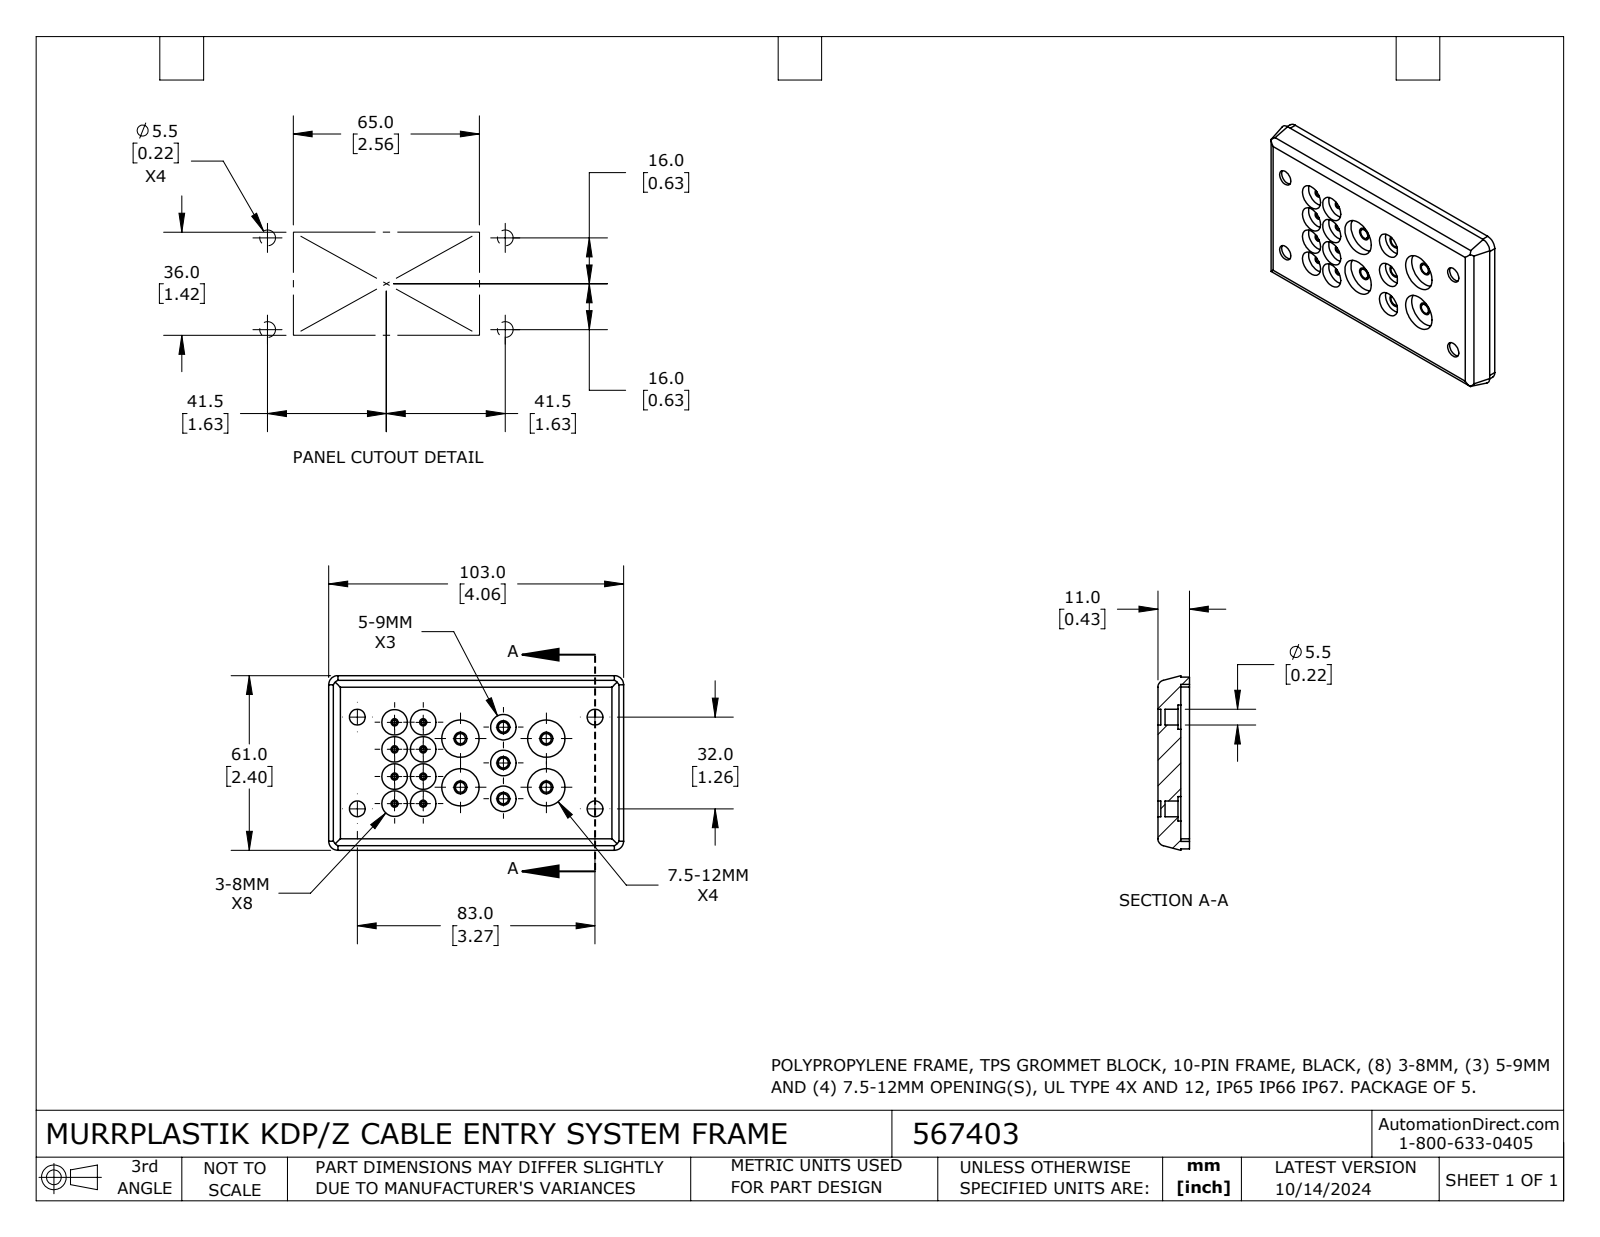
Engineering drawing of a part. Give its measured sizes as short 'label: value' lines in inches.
name: 567403
written by: SolidWorks 2023 (CONFIG_CONTROL_DESIGN)
unit: in
bodies: 1 solid, 235 faces (87 planar, 144 cylindrical, 4 other)
size: 4.055 × 2.402 × 0.433
volume: 2.245 in³; area: 31.6 in²
holes: 11× ⌀0.35, 8× ⌀0.098, 7× ⌀0.177, 4× ⌀0.217, 4× ⌀0.335, 4× ⌀0.512
bosses: 8× ⌀0.059, 7× ⌀0.138
rounds: 8× R0.012, 4× R0.035, 4× R0.098, 4× R0.138, 4× R0.244, 4× R0.266
face distances: 0.217, 0.098, 0.315, 0.118, 0.197, 0.433, 0.102, 0.386, 1.976, 2.26
hole spacings: 0.372, 0.394, 0.542, 0.611, 0.679, 0.746, 0.844, 1.016
